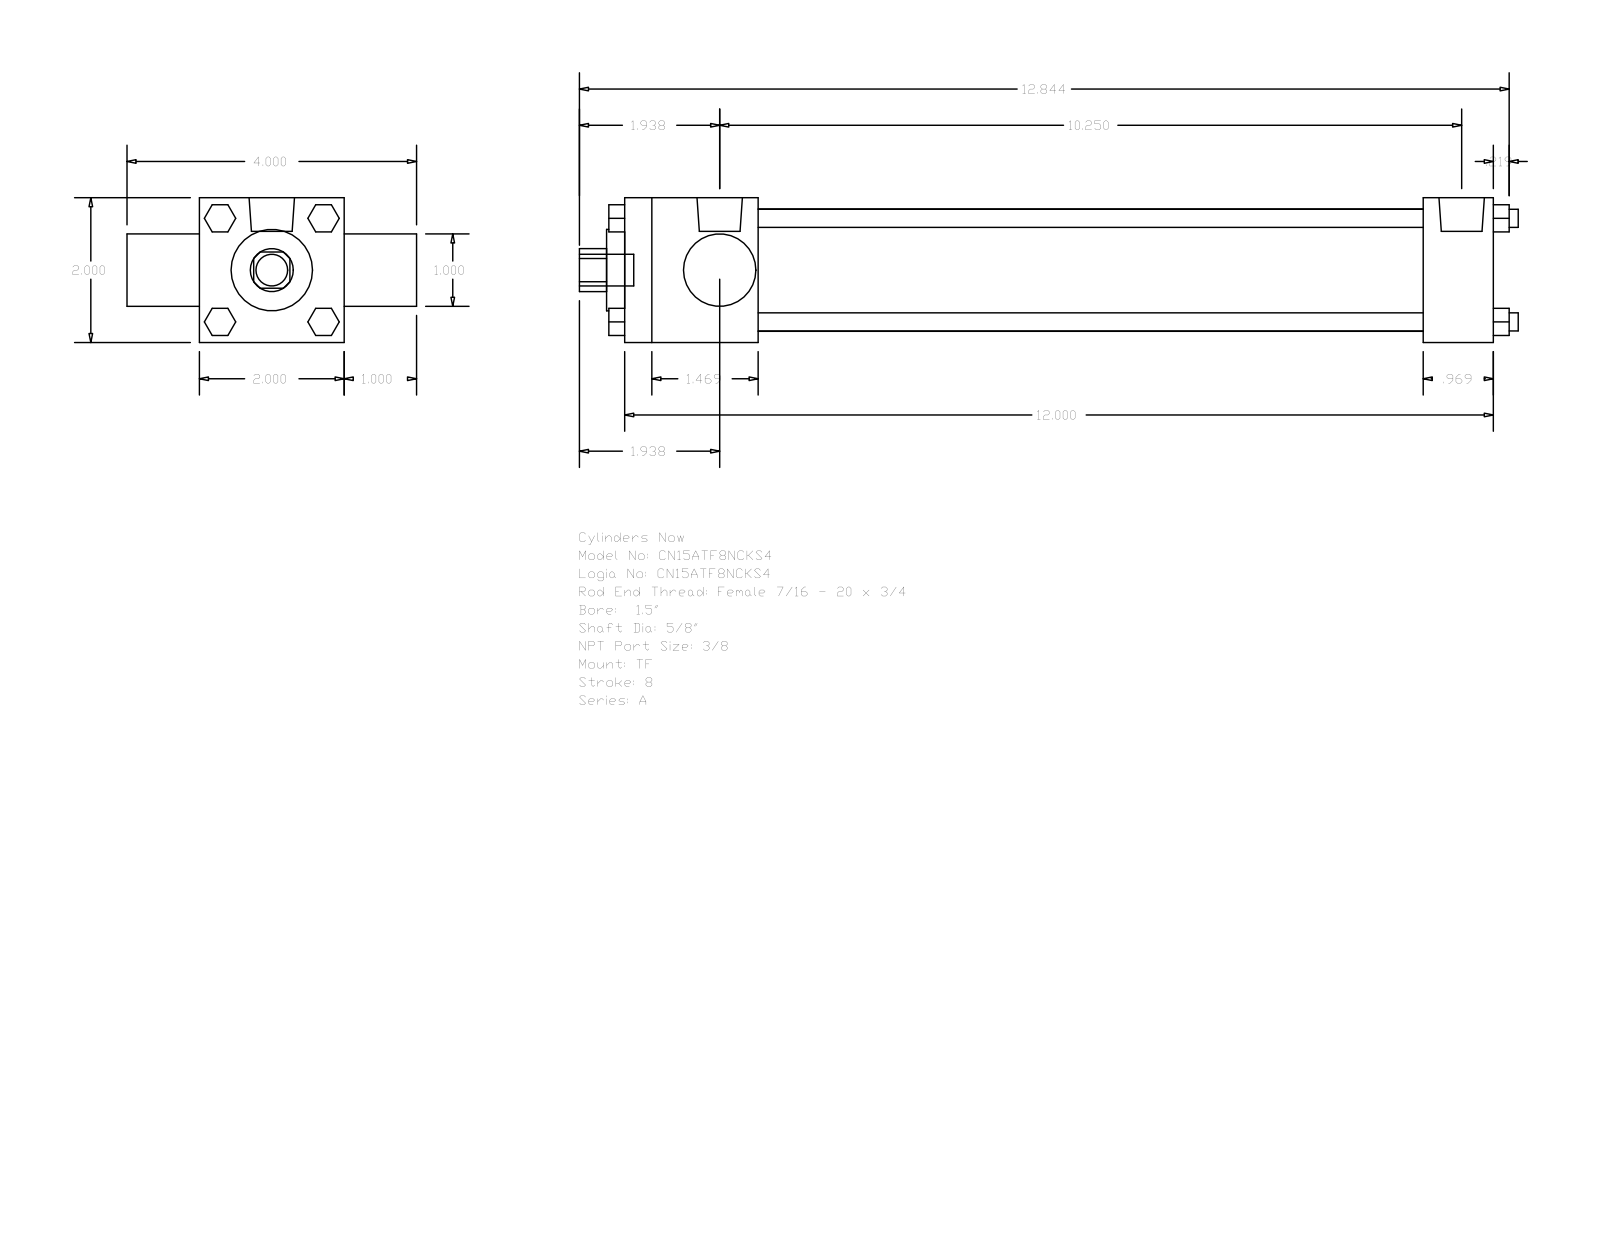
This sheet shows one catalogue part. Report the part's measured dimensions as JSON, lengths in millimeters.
{"part_name": "A_TF__0150_0.625", "step_written_by": "GSSL Pune (CONFIG_CONTROL_DESIGN)", "units": "millimeters", "bodies": {"solids": 0, "faces": 120, "planar": 92, "cylindrical": 28, "other": 0}, "overall_size": [329.41, 101.6, 50.8], "round_holes": [[15.88, 1], [25.4, 1], [28.57, 1], [42.93, 1]], "round_bosses_or_shafts": [[6.35, 4], [5.56, 3], [15.93, 2], [11.11, 1]], "partial_cylinders_radius": [[7.54, 1]], "face_to_face_distances": [50.8, 304.8, 25.4, 76.2, 46.83, 280.19, 233.36, 257.97, 24.61, 9.52]}
